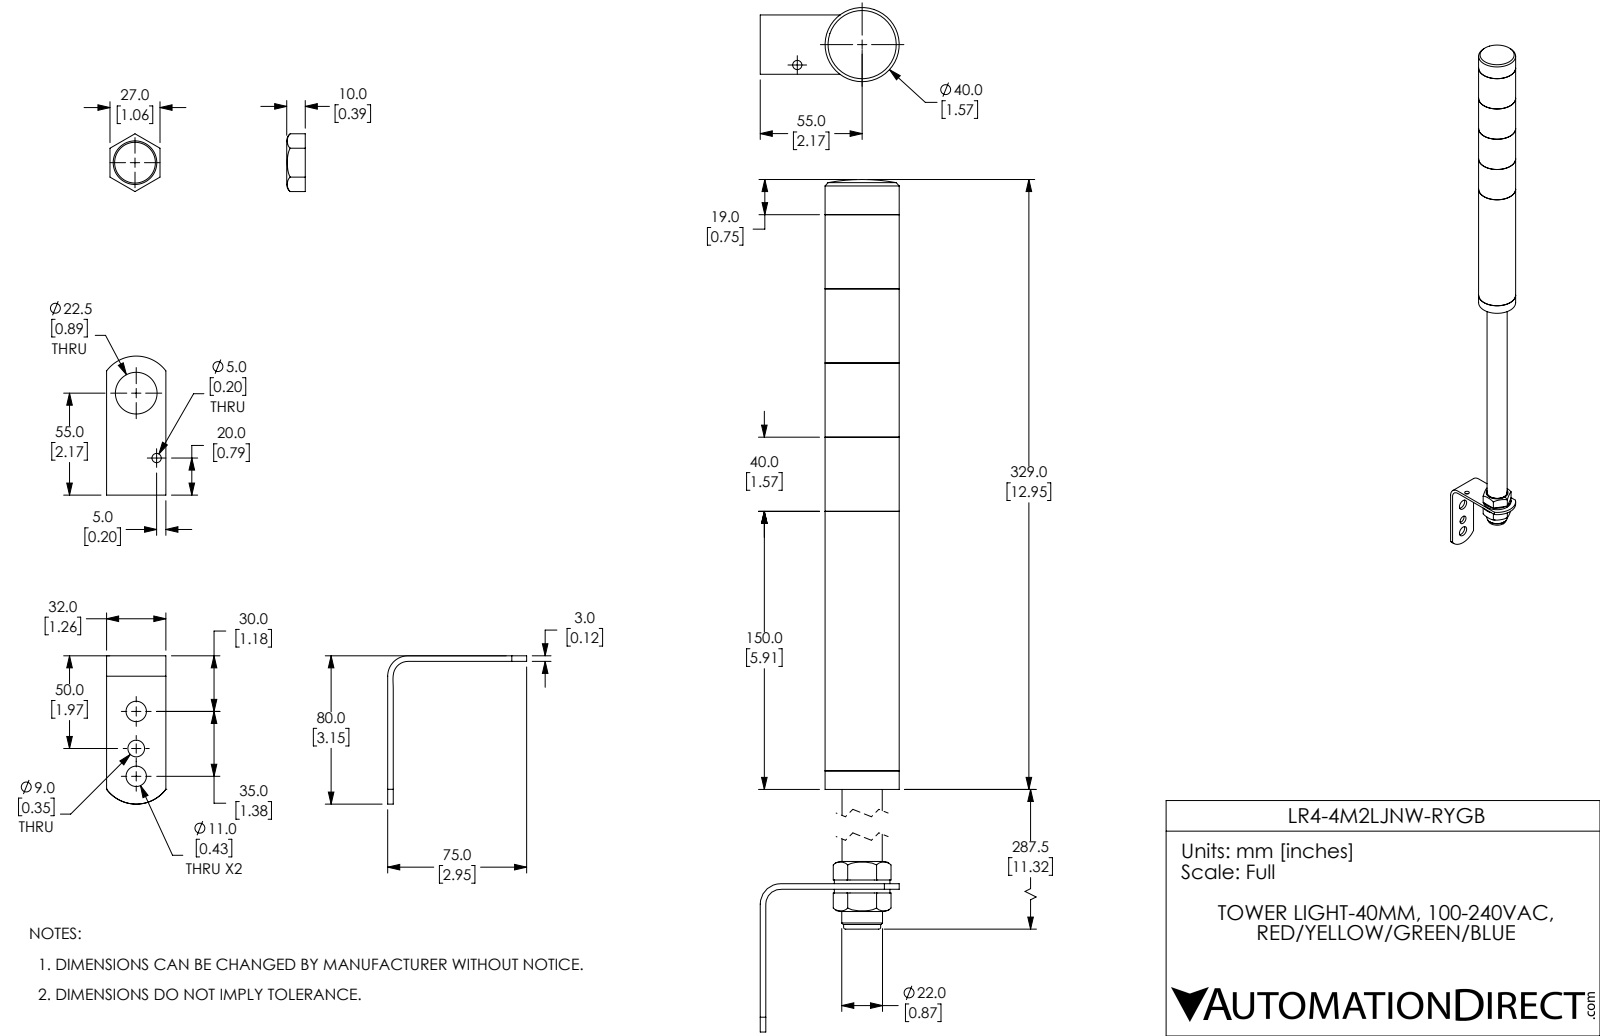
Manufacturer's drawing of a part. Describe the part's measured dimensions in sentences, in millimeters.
The part is named "LR4-4M2LJNW-RYGB". Its 3-D file was written by "SolidWorks 2017 (AUTOMOTIVE_DESIGN)". It is 13 solids with 179 faces: 64 planar, 99 cylindrical and 16 other. Overall it measures 672 by 75 by 40 millimeters. Its volume is 478 300 cubic millimeters and its surface area 130 800 square millimeters. Round holes: 2 of diameter 3.2, 2 of diameter 11, 1 of diameter 5, 1 of diameter 7.7, 1 of diameter 9, 1 of diameter 17.7, 1 of diameter 22, 1 of diameter 22.5, 1 of diameter 27.6, 1 of diameter 34.7, 1 of diameter 35.2, 1 of diameter 35.3. Round bosses or shafts: 1 of diameter 40, 1 of diameter 30, 1 of diameter 21.7. Partial cylindrical surfaces (rounded edges, fillets, slot ends): 1 of radius 20. The main face-to-face distances are 40, 80, 120, 160, 10.3, 50.3, 29.7, 136, 176, 216. The hole center spacings are 7.2, 14.4, 15, 20, 29.9, 35, 36.7, 43.6.
